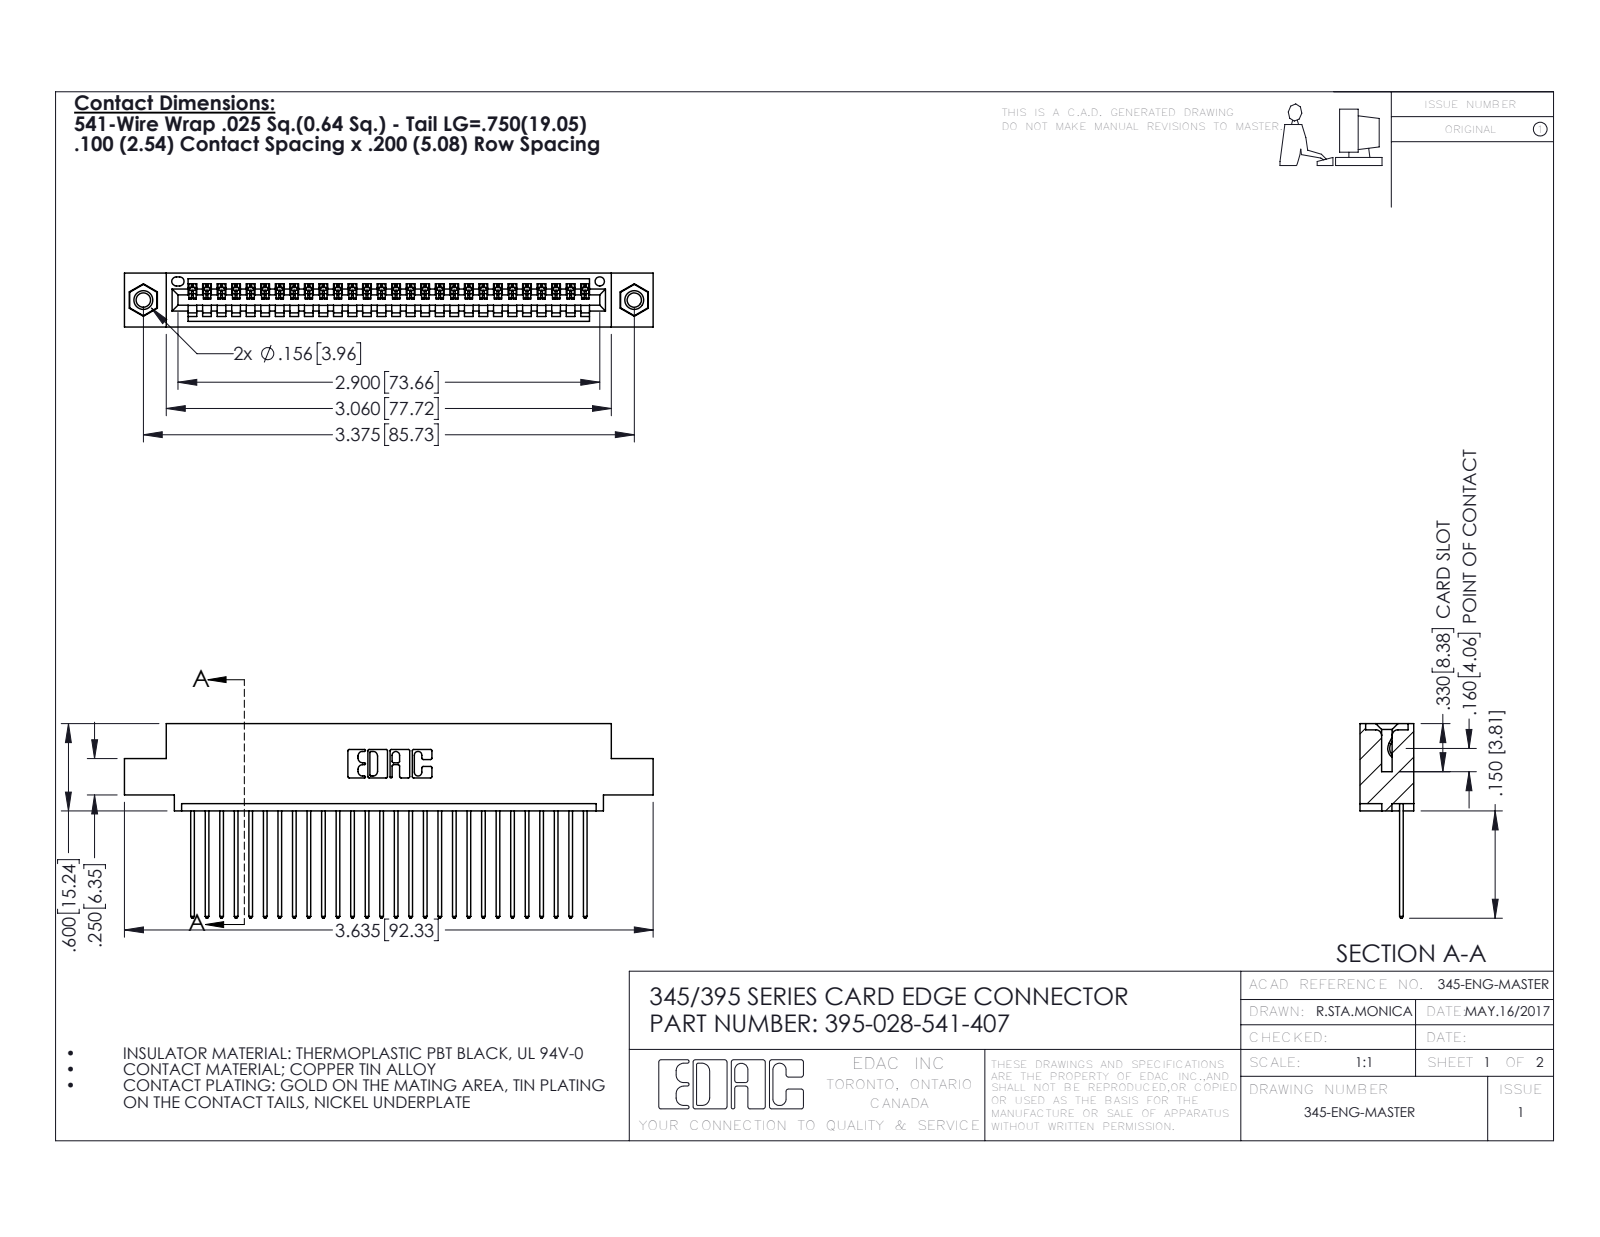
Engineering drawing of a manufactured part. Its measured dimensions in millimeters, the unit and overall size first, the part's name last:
Units: millimetres
Overall size (bounding box): 92.3 × 34 × 9.4
Round holes (diameter × count): ⌀2.5 ×2, ⌀3.2 ×2, ⌀4 ×2, ⌀1.6 ×1
Round bosses / shafts (diameter × count): ⌀3.9 ×2
Partial cylindrical surfaces — rounded edges, fillets, slot ends (radius × count): R0.2 ×56, R0.3 ×56, R0.3 ×22, R0.2 ×6, R0.8 ×6, R0.7 ×3, R0.8 ×2, R1 ×2
Main face-to-face distances: 1.8, 7.6, 9.4, 2.5, 6.9, 0.6, 5.1, 5.7, 3.8, 1.8
Hole centre spacings: 6.9, 79.8, 85.7
Volume: 8 650 mm³ · Surface area: 11 970 mm²
Bodies: 31 solids, 1814 faces (1236 planar, 562 cylindrical, 16 other)
Part name (STEP PRODUCT): 395-028-541-407; 345-250-001_345-250-005-103; 345-292-001_345-293-141; 345 Part_0.110 Offset - 0.156 Dia-TI
STEP written by: SolidWorks 2016 (CONFIG_CONTROL_DESIGN)
